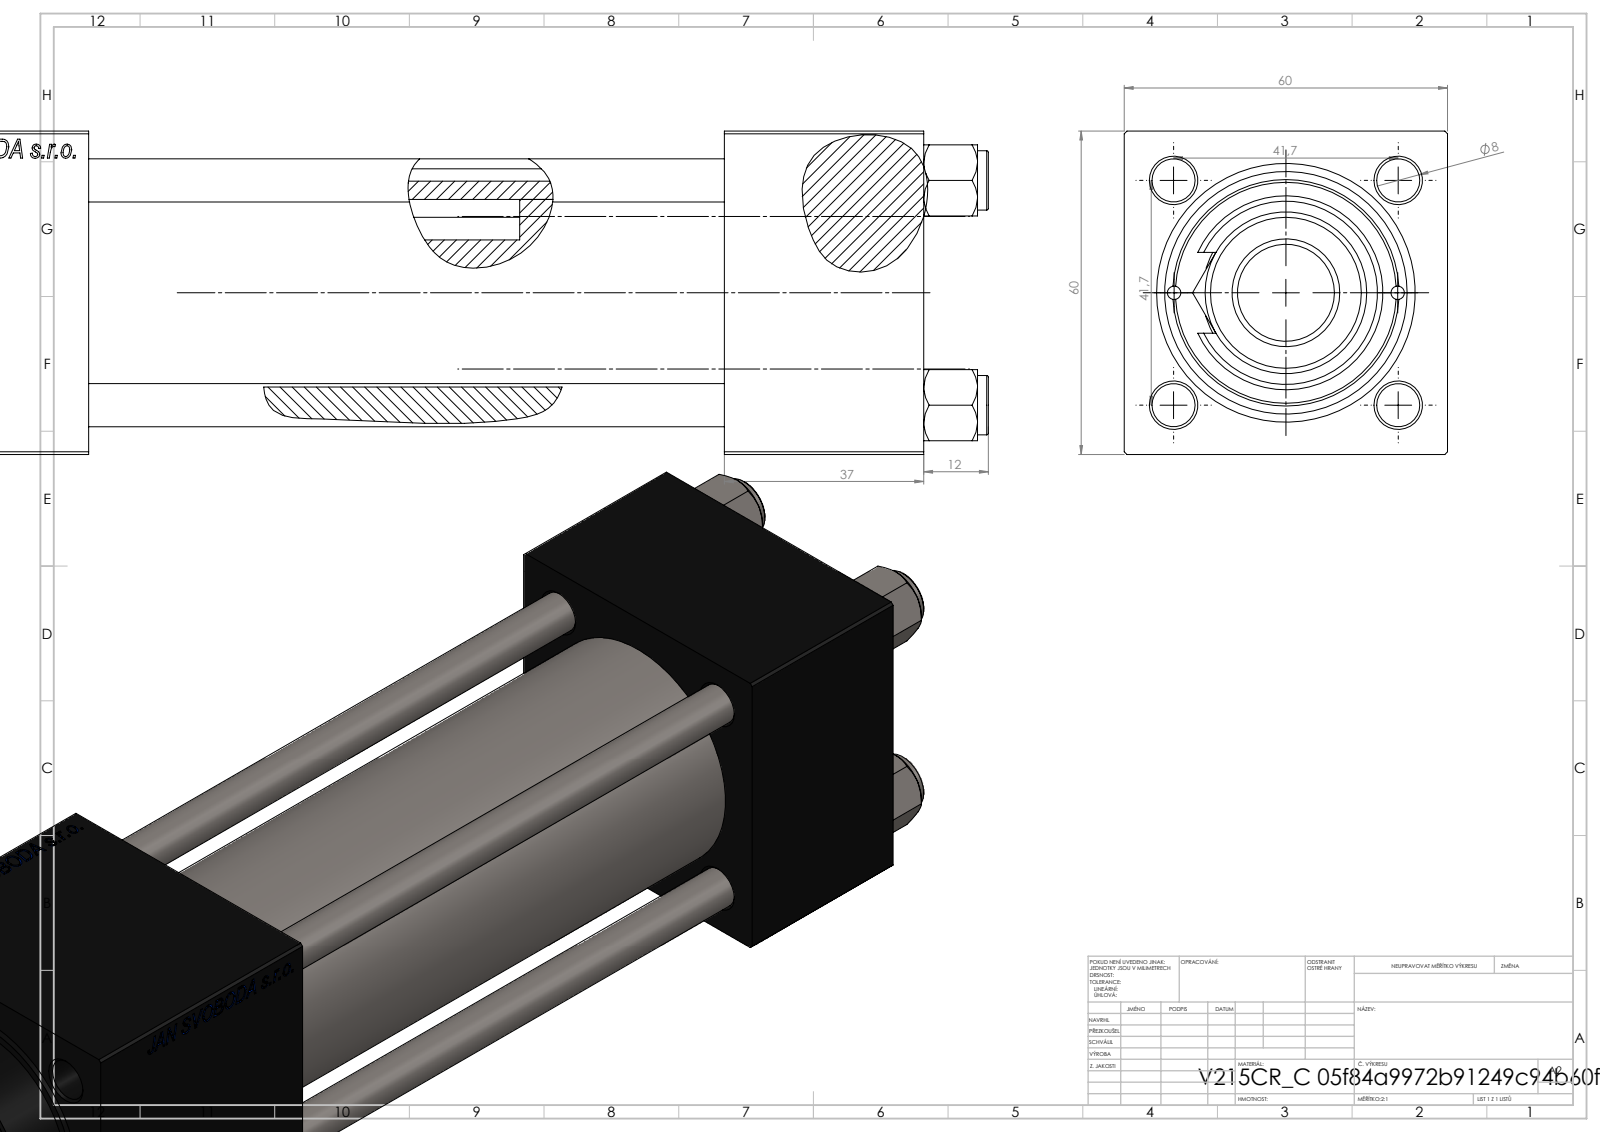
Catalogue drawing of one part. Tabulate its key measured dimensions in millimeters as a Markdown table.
| quantity | value |
| --- | --- |
| part name | V215_VC_A; FEMALE_PART_FOR_DFA; NUT_M5_C; V215CR_VCP_C (+3 more) |
| STEP written by | SolidWorks 2019 (CONFIG_CONTROL_DESIGN) |
| units | millimeters |
| bodies | 13 solids, 1239 faces (556 planar, 103 cylindrical, 580 other) |
| overall size | 329 × 60 × 60 |
| volume | 546 305 mm³ |
| surface area | 152 319 mm² |
| round holes (diameter × count) | 8 × 4, 2.5 × 2, 7 × 2, 16.66 × 2, 24 × 2, 18.5 × 1, 28 × 1, 31 × 1, 40 × 1, 45 × 1 |
| round bosses / shafts (diameter × count) | 11 × 4, 46 × 1, 42 × 1, 36 × 1, 30 × 1, 22 × 1, 20 × 1, 18 × 1 |
| partial cylindrical surfaces (radius × count) | 7.5 × 1, 12 × 1, 13.5 × 1 |
| main face-to-face distances | 60, 37, 53, 155, 118, 179.3, 142.3, 24.3, 208, 171 |
| hole center spacings | 20.85, 29.49, 41.7, 46.53, 20.75, 58.97, 41.5, 152.5 |
